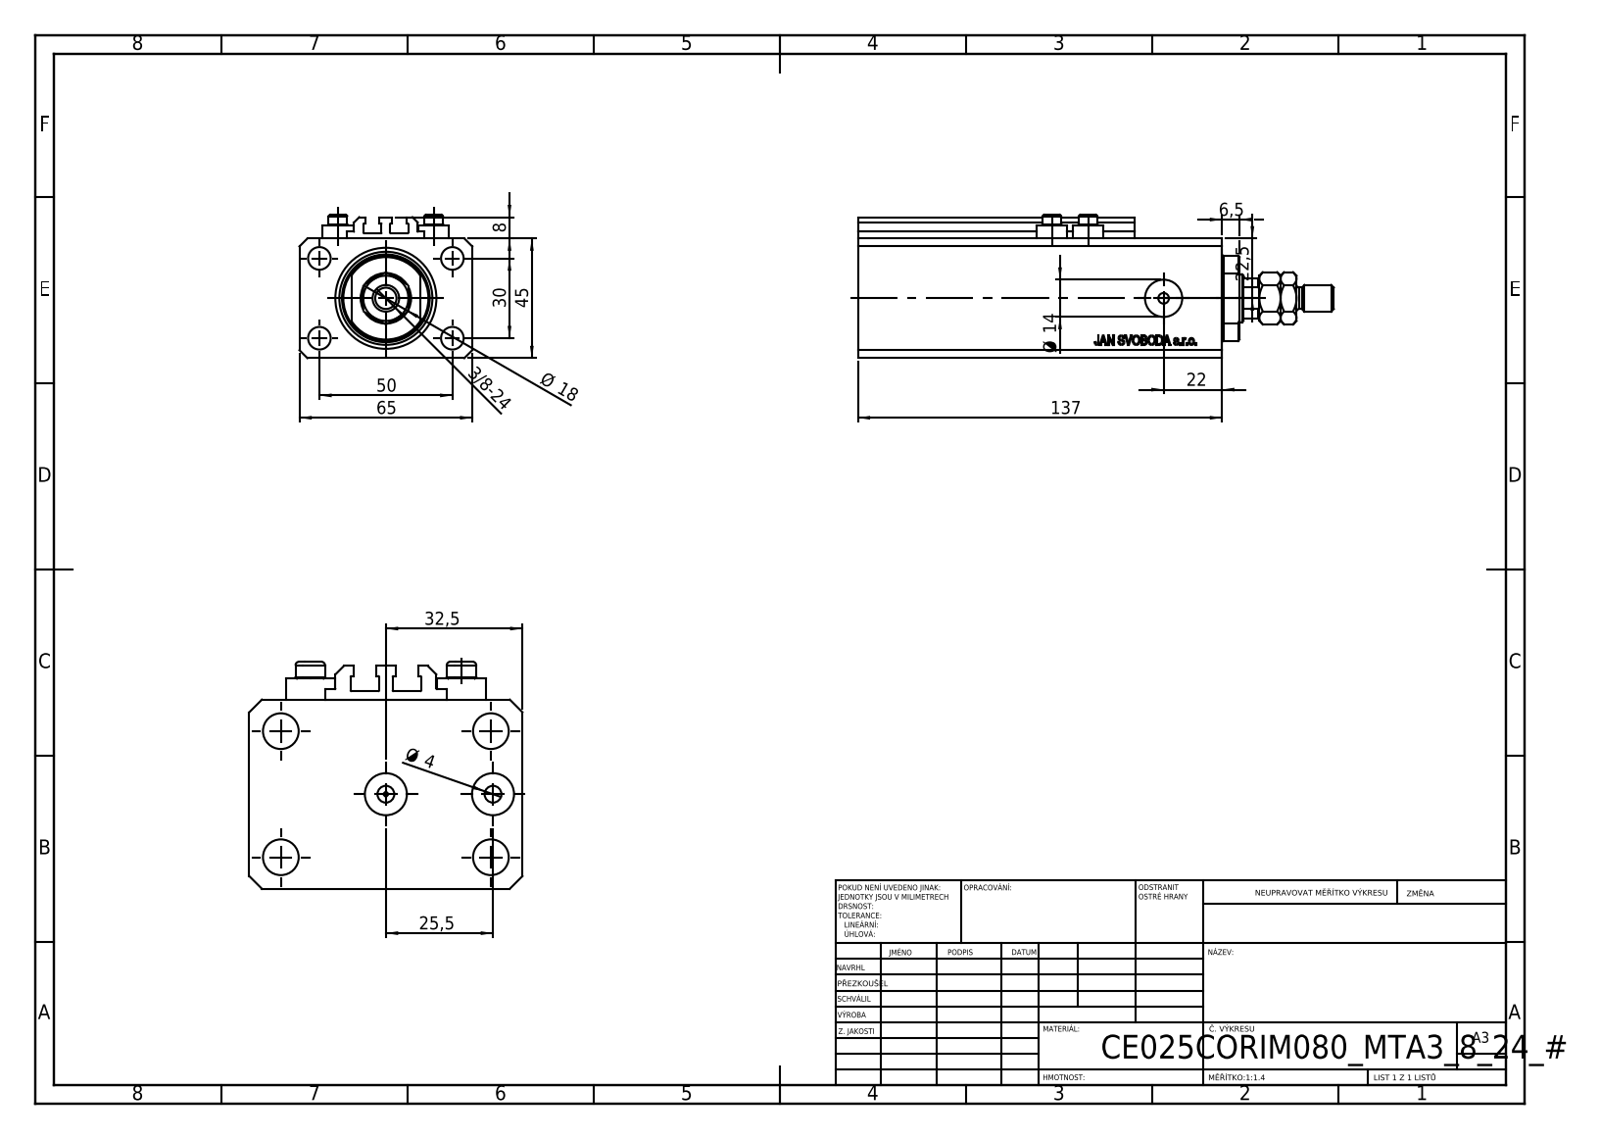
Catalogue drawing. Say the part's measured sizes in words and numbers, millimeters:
The part is named "V250CE_VC_C; V250CE_C_Body; V250CE_C_VCP; MTA (+1 more)". Its 3-D file was written by "SolidWorks 2019 (CONFIG_CONTROL_DESIGN)". It is 9 solids with 1087 faces: 519 planar, 92 cylindrical and 476 other. Overall it measures 179 by 65 by 54 millimeters. Its volume is 370 133 cubic millimeters and its surface area 92 823 square millimeters. Round holes: 8 of diameter 4, 5 of diameter 8.5, 2 of diameter 10, 2 of diameter 14, 1 of diameter 1.25, 1 of diameter 18, 1 of diameter 25, 1 of diameter 38. Round bosses or shafts: 4 of diameter 11.6, 4 of diameter 7, 1 of diameter 8. Partial cylindrical surfaces (rounded edges, fillets, slot ends): 10 of radius 0.2, 1 of radius 8.5, 1 of radius 16. The main face-to-face distances are 45, 65, 14, 47, 137, 123, 2.5, 2, 6, 10. The hole center spacings are 29.15, 13.6, 15.01, 30, 36, 38.48, 50, 52.68.
